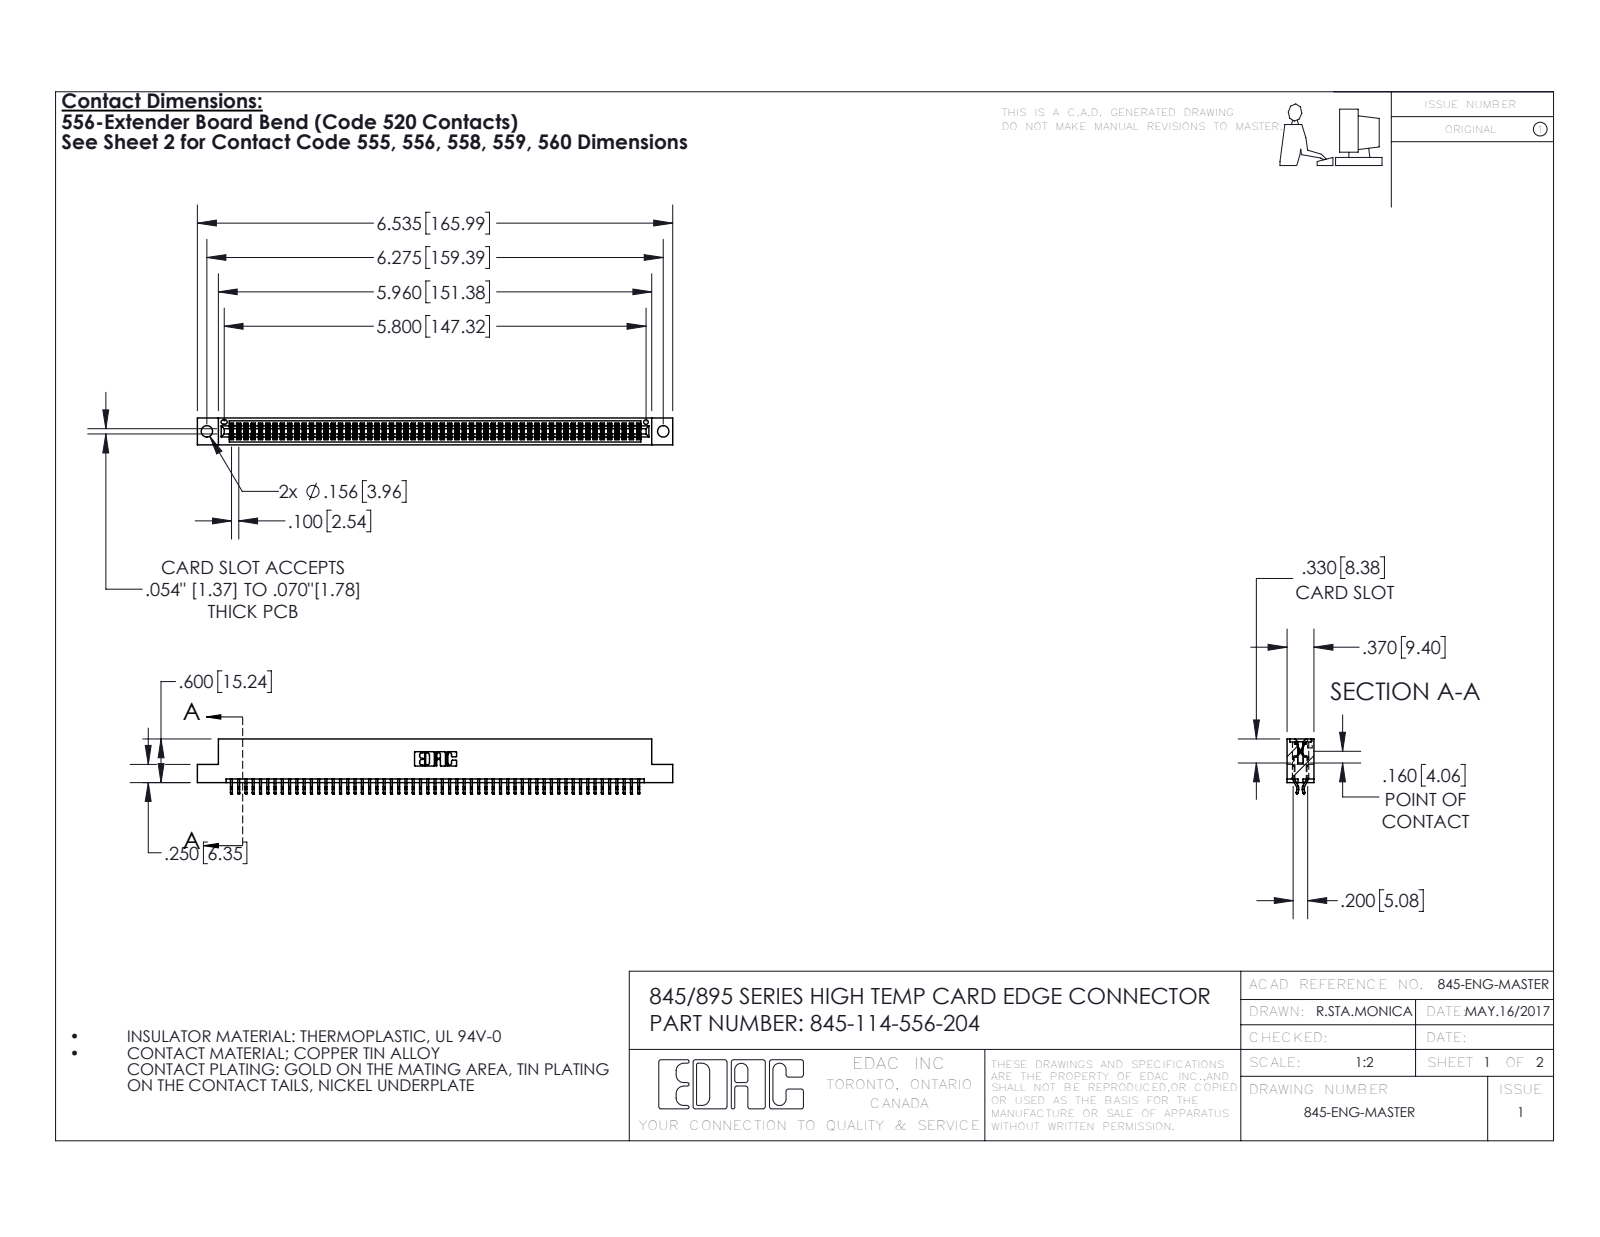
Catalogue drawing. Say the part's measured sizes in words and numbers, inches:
The part is named "345-292-001_556 Tail; 345 Part_Flush Mounting Lugs - 0.156 Dia-TH; 345-114-556-204". Its 3-D file was written by "SolidWorks 2016 (CONFIG_CONTROL_DESIGN)". It is 115 solids with 6510 faces: 4298 planar, 2212 cylindrical and 0 other. Overall it measures 6.535 by 0.757 by 0.37 inches. Its volume is 0.987 cubic inches and its surface area 37.06 square inches. Round holes: 2 of diameter 0.156, 1 of diameter 0.064. Partial cylindrical surfaces (rounded edges, fillets, slot ends): 171 of radius 0.006, 22 of radius 0.01, 6 of radius 0.007, 6 of radius 0.031, 3 of radius 0.026, 2 of radius 0.01, 2 of radius 0.014, 2 of radius 0.019. The main face-to-face distances are 0.298, 0.072, 0.37, 0.2, 0.025, 0.098, 0.272, 0.225, 0.175, 0.149. The hole center spacings are 0.27, 6.039, 6.275.
